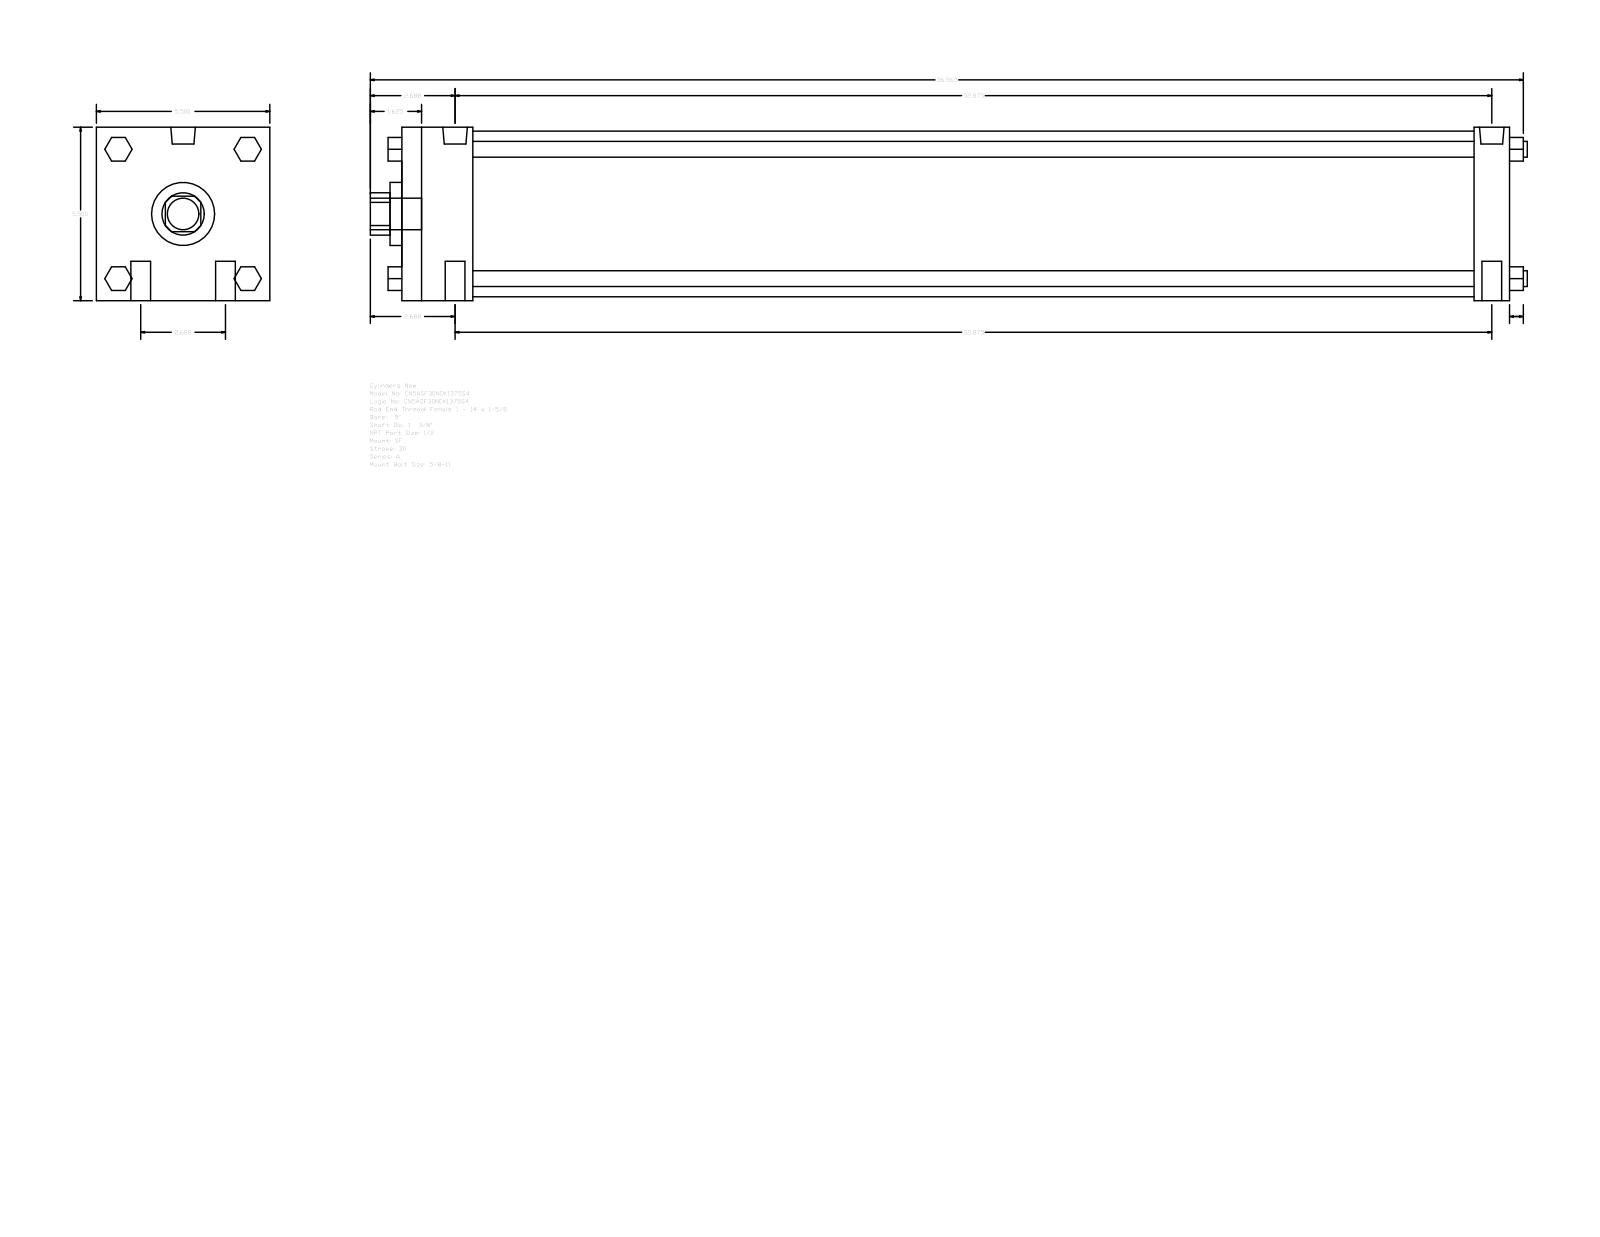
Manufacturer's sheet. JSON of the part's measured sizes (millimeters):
{"part_name": "A_SF__0500_1.375", "step_written_by": "GSSL Pune (CONFIG_CONTROL_DESIGN)", "units": "millimeters", "bodies": {"solids": 0, "faces": 124, "planar": 94, "cylindrical": 30, "other": 0}, "overall_size": [931.86, 139.7, 139.7], "round_holes": [[34.92, 1], [50.8, 1], [133.35, 1]], "round_bosses_or_shafts": [[15.88, 4], [12.7, 4], [19.77, 2], [8.73, 2], [25.4, 1]], "partial_cylinders_radius": [[17.06, 1]], "face_to_face_distances": [139.7, 892.18, 28.58, 57.15, 863.6, 806.45, 835.03, 19.05, 52.07, 90.18]}
